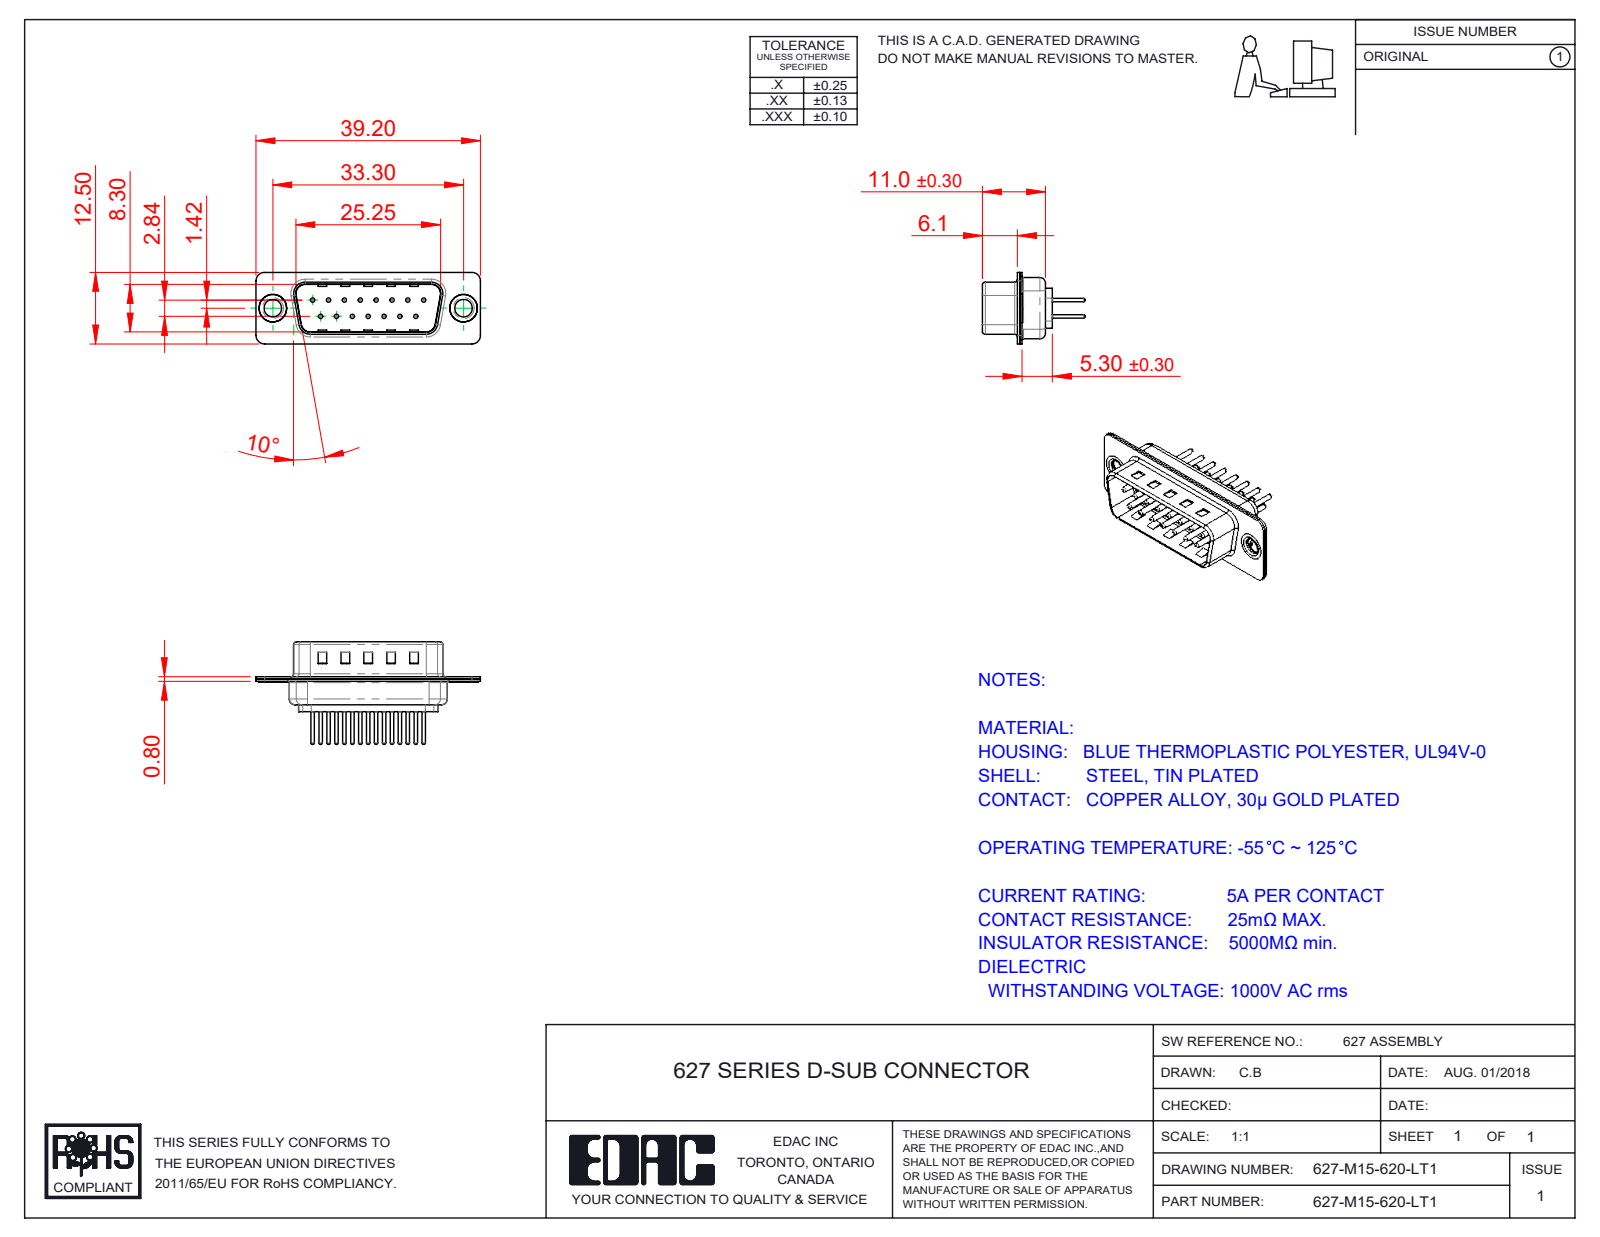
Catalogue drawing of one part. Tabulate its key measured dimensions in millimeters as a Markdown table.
| quantity | value |
| --- | --- |
| part name | 627M Housing_15 Contacts; 627M Thru Hole Rivet; 627M Contact Row 2_20; 627M Shell Rear_15 Contacts (+3 more) |
| STEP written by | SolidWorks 2020 (CONFIG_CONTROL_DESIGN) |
| units | millimeters |
| bodies | 20 solids, 869 faces (244 planar, 327 cylindrical, 298 other) |
| overall size | 39.2 × 17.9 × 12.5 |
| volume | 1 765 mm³ |
| surface area | 4 663 mm² |
| round holes (diameter × count) | 0.75 × 15, 1.6 × 15, 2 × 15, 3.05 × 2, 4 × 2, 4.8 × 2 |
| round bosses / shafts (diameter × count) | 1.5 × 15, 0.6 × 15, 5 × 2, 4.9 × 2, 3.55 × 2 |
| partial cylindrical surfaces (radius × count) | 1.5 × 16, 2 × 12, 0.5 × 8, 1.6 × 8, 0.25 × 4, 0.6 × 4, 0.65 × 4, 0.9 × 4 |
| main face-to-face distances | 0.4, 0.8, 9.5, 9.1, 8.7, 9.9, 1.2, 6.1, 5.7, 5.3 |
| hole center spacings | 3.16, 2.77, 5.54, 8.31, 11.08, 5.03, 5.04, 7.48 |
